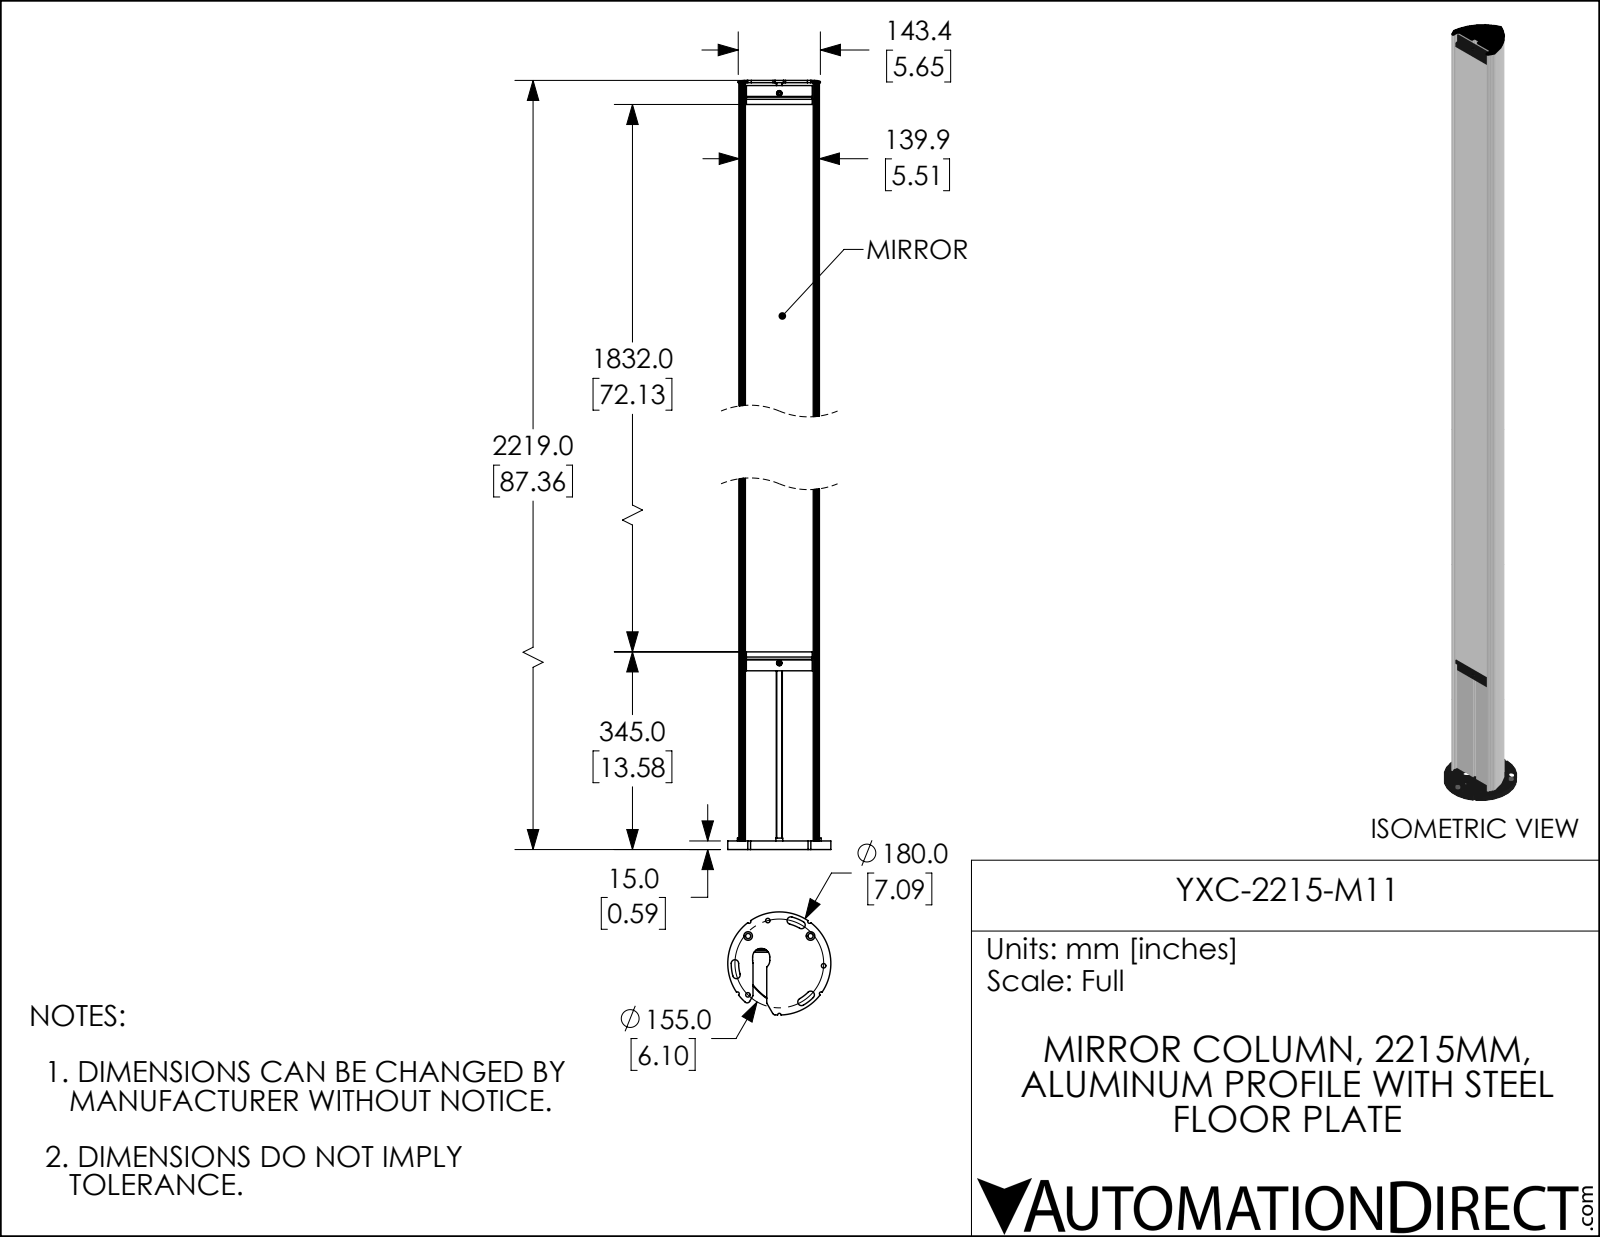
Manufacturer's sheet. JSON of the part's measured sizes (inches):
{"part_name": "YXC-2215-M11", "step_written_by": "SolidWorks 2019 (AUTOMOTIVE_DESIGN)", "units": "inches", "bodies": {"solids": 1, "faces": 290, "planar": 187, "cylindrical": 88, "other": 15}, "overall_size": [87.362, 7.087, 7.085], "volume_in3": 1278, "surface_area_in2": 1781, "round_holes": [[0.307, 3], [0.591, 3], [0.354, 2], [0.173, 1]], "round_bosses_or_shafts": [[0.472, 3], [0.374, 2], [0.335, 2], [7.087, 1]], "partial_cylinders_radius": [[0.118, 9], [0.256, 6], [0.236, 5], [0.039, 4], [0.052, 4], [4.685, 4], [0.197, 3], [0.052, 2]], "face_to_face_distances": [0.157, 0.118, 0.335, 0.492, 0.453, 0.591, 0.098, 0.382, 0.224, 0.11], "hole_center_spacings": [2.146, 1.255, 1.257, 1.722, 2.235, 3.121, 3.717, 3.719]}
